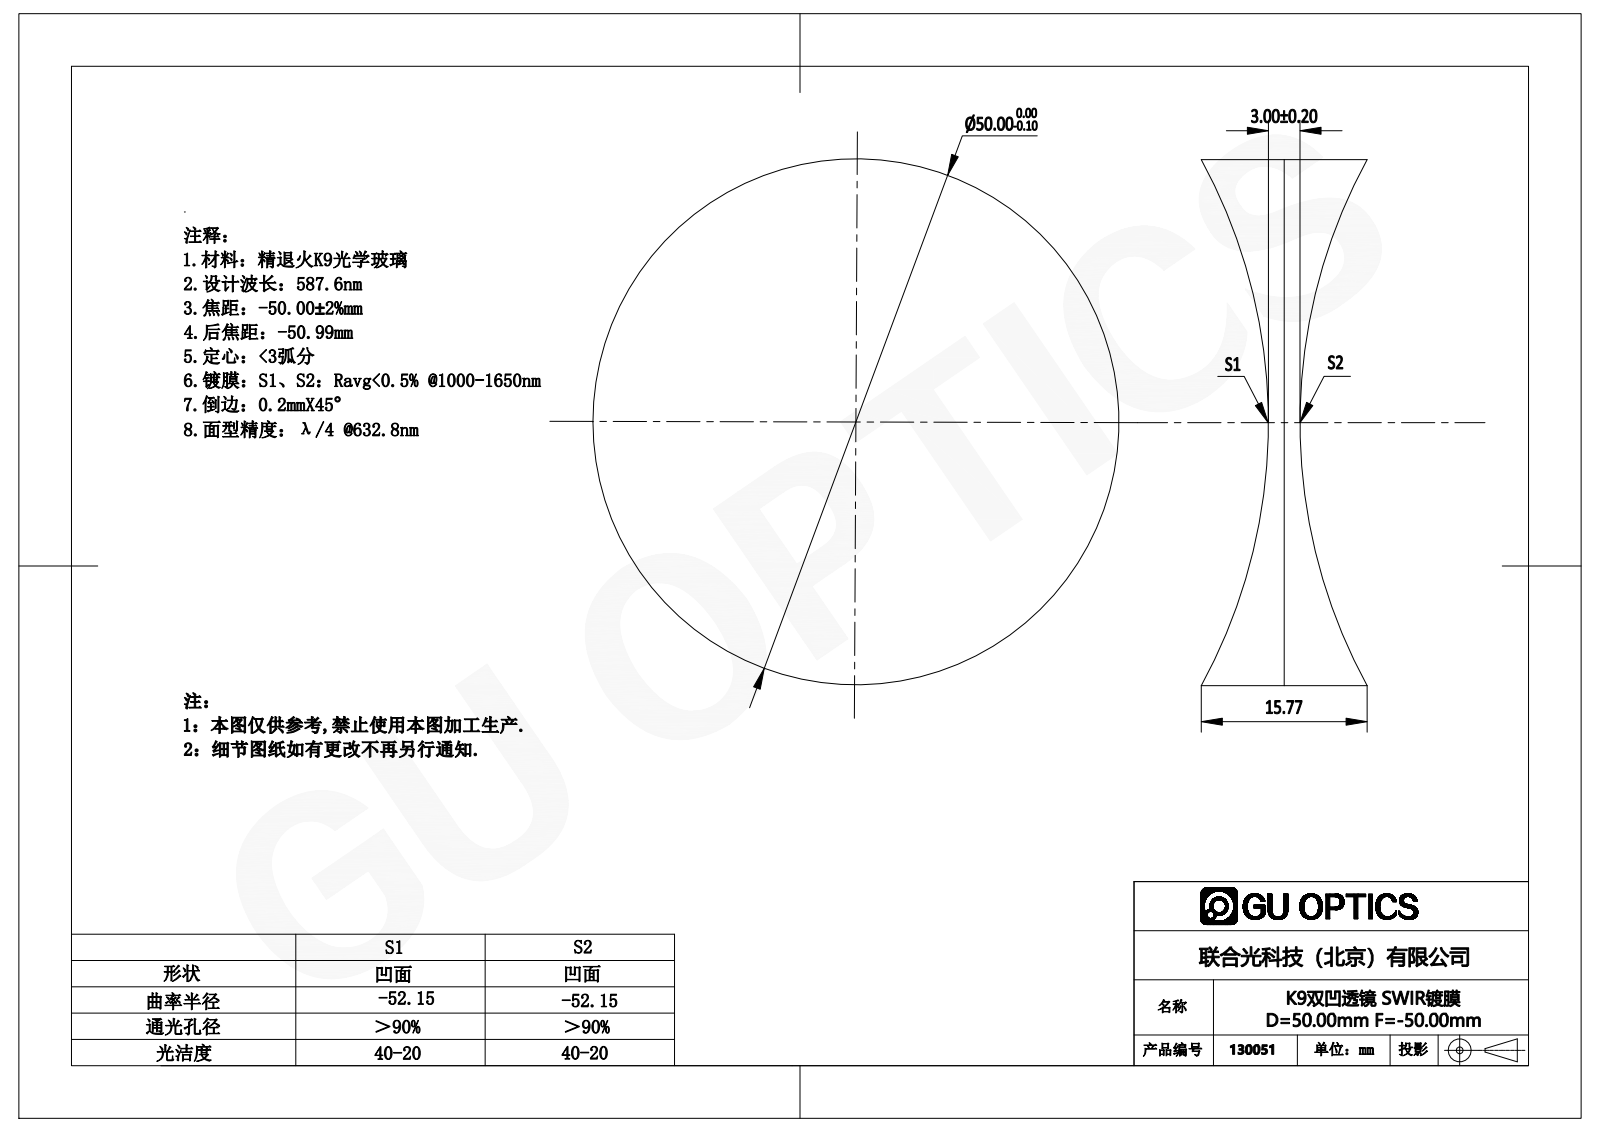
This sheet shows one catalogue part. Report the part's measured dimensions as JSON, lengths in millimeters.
{"part_name": "130012", "step_written_by": "SolidWorks 2016 (AUTOMOTIVE_DESIGN)", "units": "millimeters", "bodies": {"solids": 1, "faces": 6, "planar": 0, "cylindrical": 2, "other": 4}, "overall_size": [50, 50, 15.77], "volume_mm3": 18151, "surface_area_mm2": 6659, "round_bosses_or_shafts": [[50, 1]]}
